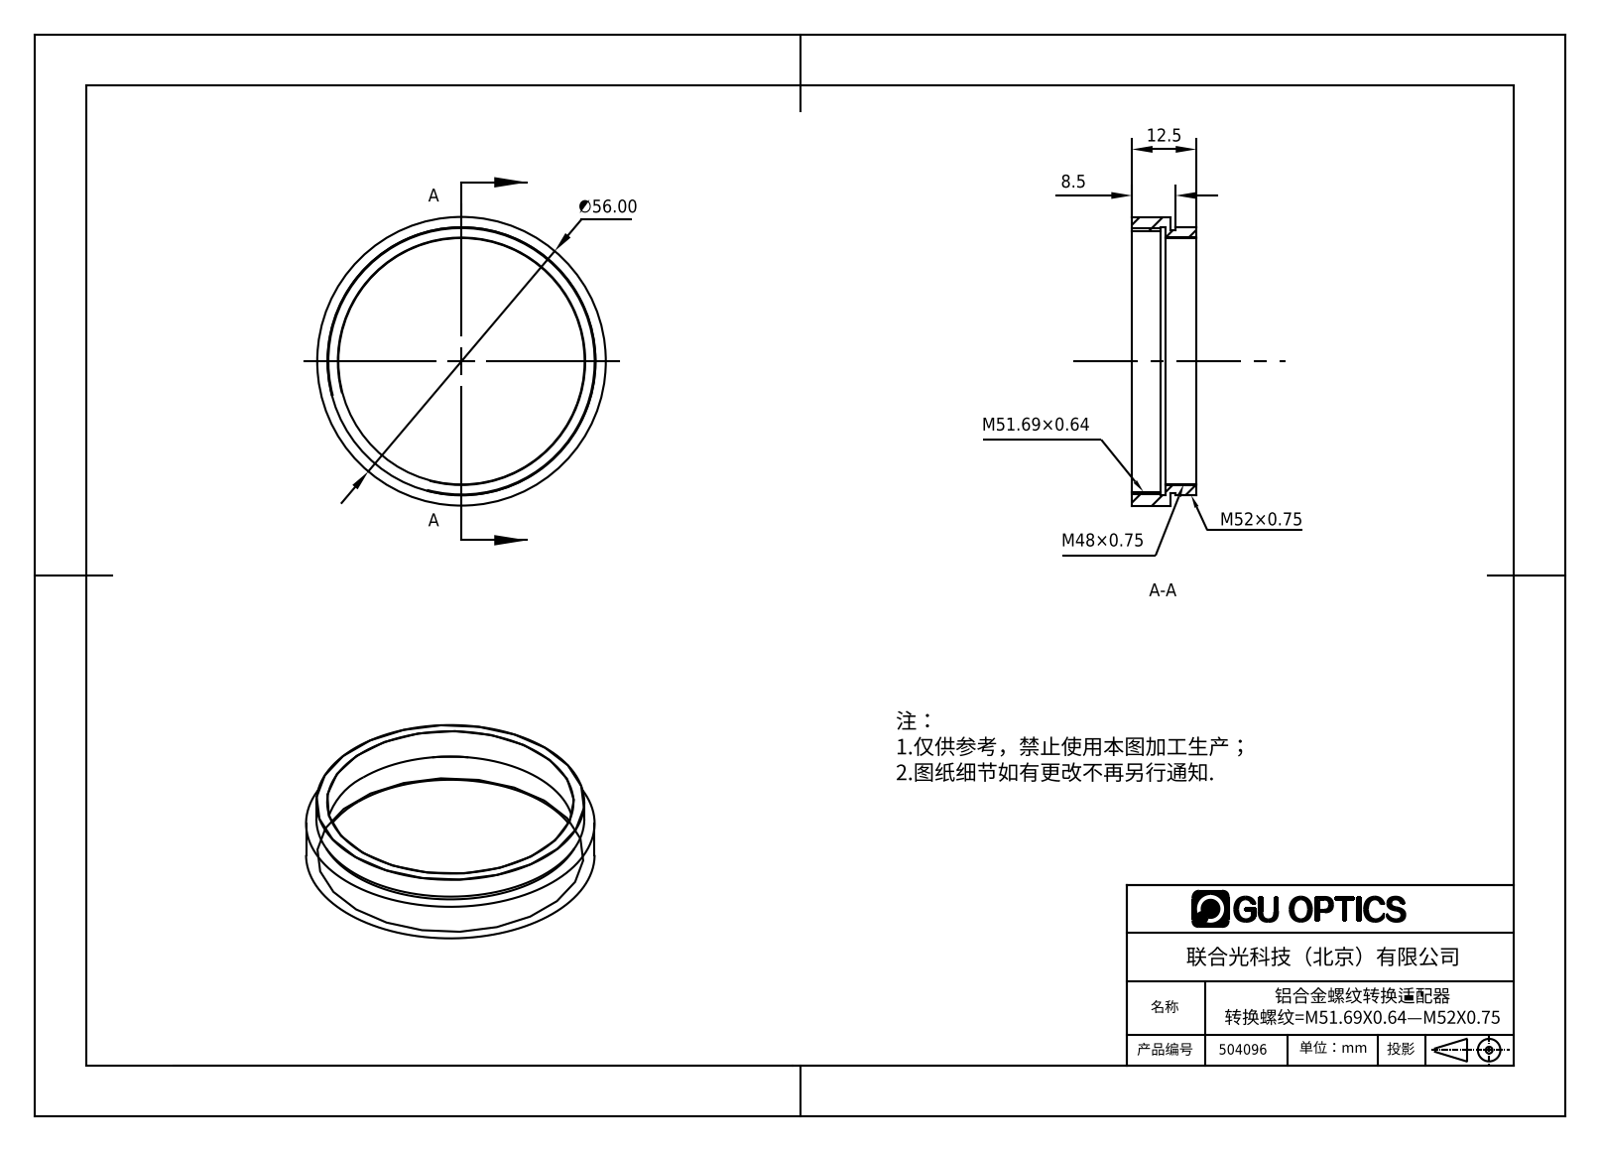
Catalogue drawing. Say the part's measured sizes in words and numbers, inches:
The part is named "504096". Its 3-D file was written by "SolidWorks 2016 (AUTOMOTIVE_DESIGN)". It is 1 solid with 18 faces: 6 planar, 12 cylindrical and 0 other. Overall it measures 2.205 by 2.205 by 0.492 inches. Its volume is 0.309 cubic inches and its surface area 8.959 square inches. Round holes: 1 of diameter 1.882, 1 of diameter 1.992, 1 of diameter 2.043. Round bosses or shafts: 1 of diameter 2.205, 1 of diameter 2.047, 1 of diameter 2.008. The main face-to-face distances are 0.039, 0.295, 0.492, 0.197, 0.256, 0.236, 0.079, 0.217, 0.276, 0.335.
